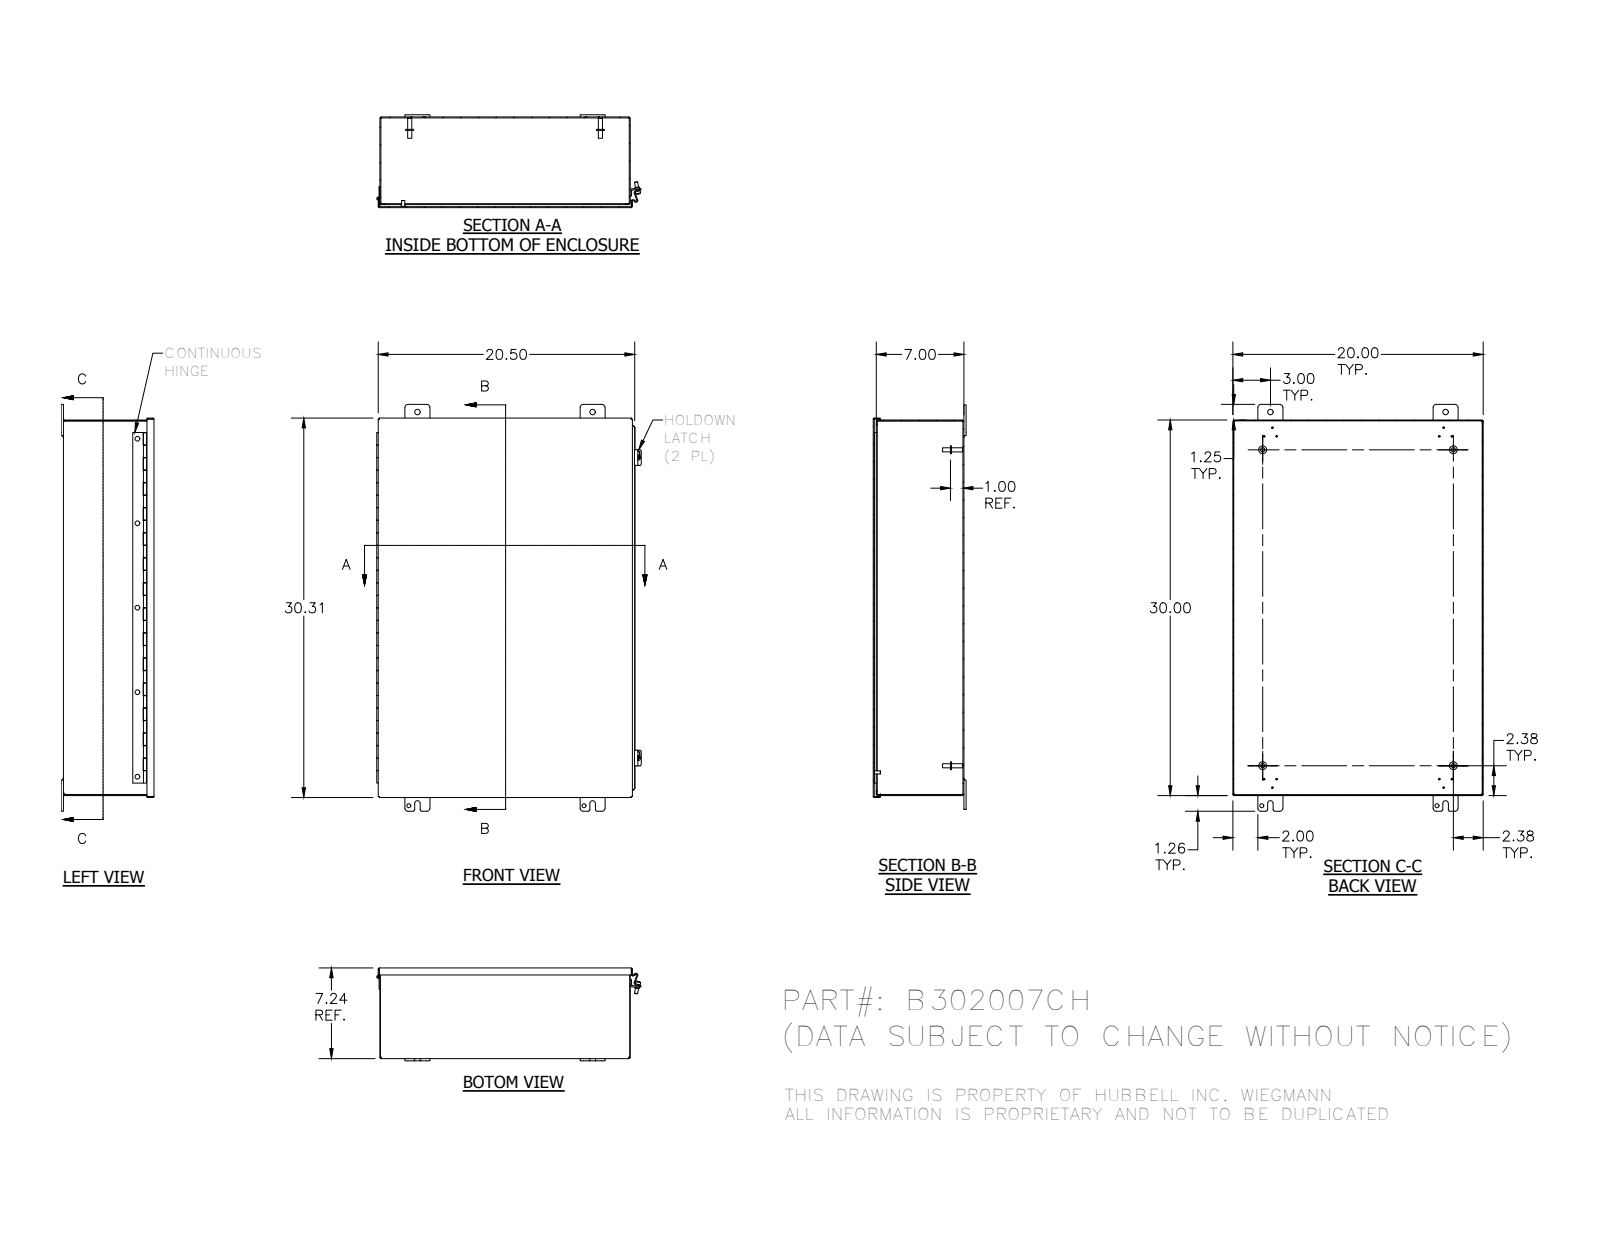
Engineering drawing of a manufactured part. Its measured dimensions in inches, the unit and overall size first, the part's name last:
Units: inches
Overall size (bounding box): 32.505 × 21.136 × 7.423
Round holes (diameter × count): ⌀0.375 ×5, ⌀0.11 ×4, ⌀0.313 ×4, ⌀0.438 ×4, ⌀0.196 ×2, ⌀0.125 ×1, ⌀0.125 ×1
Round bosses / shafts (diameter × count): ⌀0.625 ×4, ⌀0.33 ×4, ⌀0.25 ×4, ⌀0.41 ×2, ⌀0.344 ×2, ⌀0.337 ×1, ⌀0.12 ×1
Partial cylindrical surfaces — rounded edges, fillets, slot ends (radius × count): R0.125 ×16, R0.25 ×16, R0.031 ×8, R0.063 ×8, R0.07 ×8, R0.105 ×8, R0.016 ×5, R0.09 ×5
Main face-to-face distances: 0.074, 7.169, 7.243, 7.095, 19.926, 29.926, 20, 19.852, 30, 29.852
Hole centre spacings: 1.593, 6.75, 14, 30.005, 33.111, 13.5, 0.75, 1.134
Volume: 154.9 in³ · Surface area: 4 183 in²
Bodies: 20 solids, 698 faces (431 planar, 198 cylindrical, 69 other)
Part name (STEP PRODUCT): B302007CH; B302007CHBKP; B3020CHLID; H6010102 (+8 more)
STEP written by: Autodesk Inventor 2012 (AUTOMOTIVE_DESIGN)
